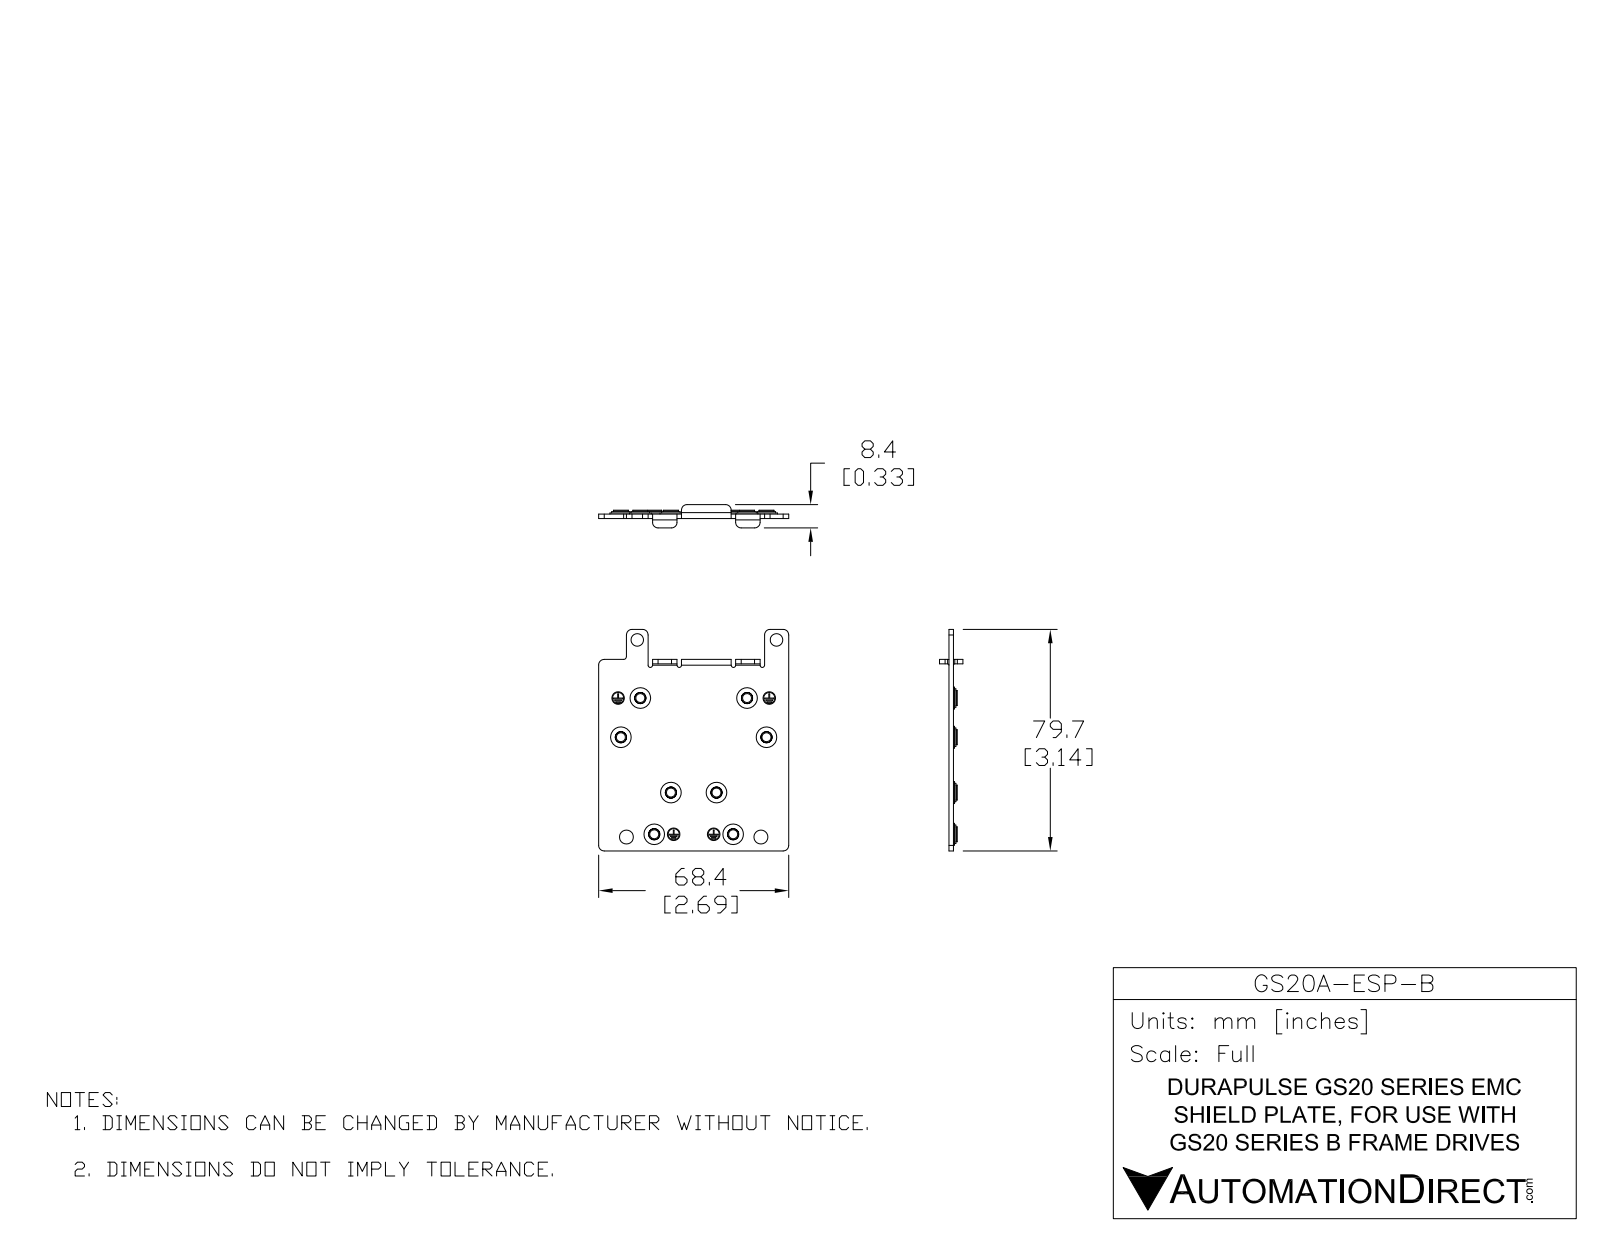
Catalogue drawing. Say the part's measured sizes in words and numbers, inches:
The part is named "GS20A-ESP-B b". Its 3-D file was written by "SolidWorks 2017 (AUTOMOTIVE_DESIGN)". It is 15 solids with 664 faces: 278 planar, 174 cylindrical and 212 other. Overall it measures 3.138 by 2.665 by 0.91 inches. Its volume is 0.657 cubic inches and its surface area 31.91 square inches. Round holes: 8 of diameter 0.128, 8 of diameter 0.213, 4 of diameter 0.213, 4 of diameter 0.315, 2 of diameter 0.177, 2 of diameter 0.197. Round bosses or shafts: 8 of diameter 0.31, 8 of diameter 0.212, 4 of diameter 0.283, 4 of diameter 0.261, 4 of diameter 0.261, 2 of diameter 0.315, 2 of diameter 0.272, 2 of diameter 0.157. Partial cylindrical surfaces (rounded edges, fillets, slot ends): 13 of radius 0.079, 8 of radius 0.106, 8 of radius 0.295, 6 of radius 0.02, 4 of radius 0.199, 4 of radius 0.219, 2 of radius 0.083, 1 of radius 0.039. The main face-to-face distances are 0.063, 0.02, 0.083, 0.663, 0.683, 0.644, 1.327, 1.24, 0.07, 0.133. The hole center spacings are 0.335, 0.354, 0.396, 0.561, 0.599, 0.62, 0.636, 0.73.
